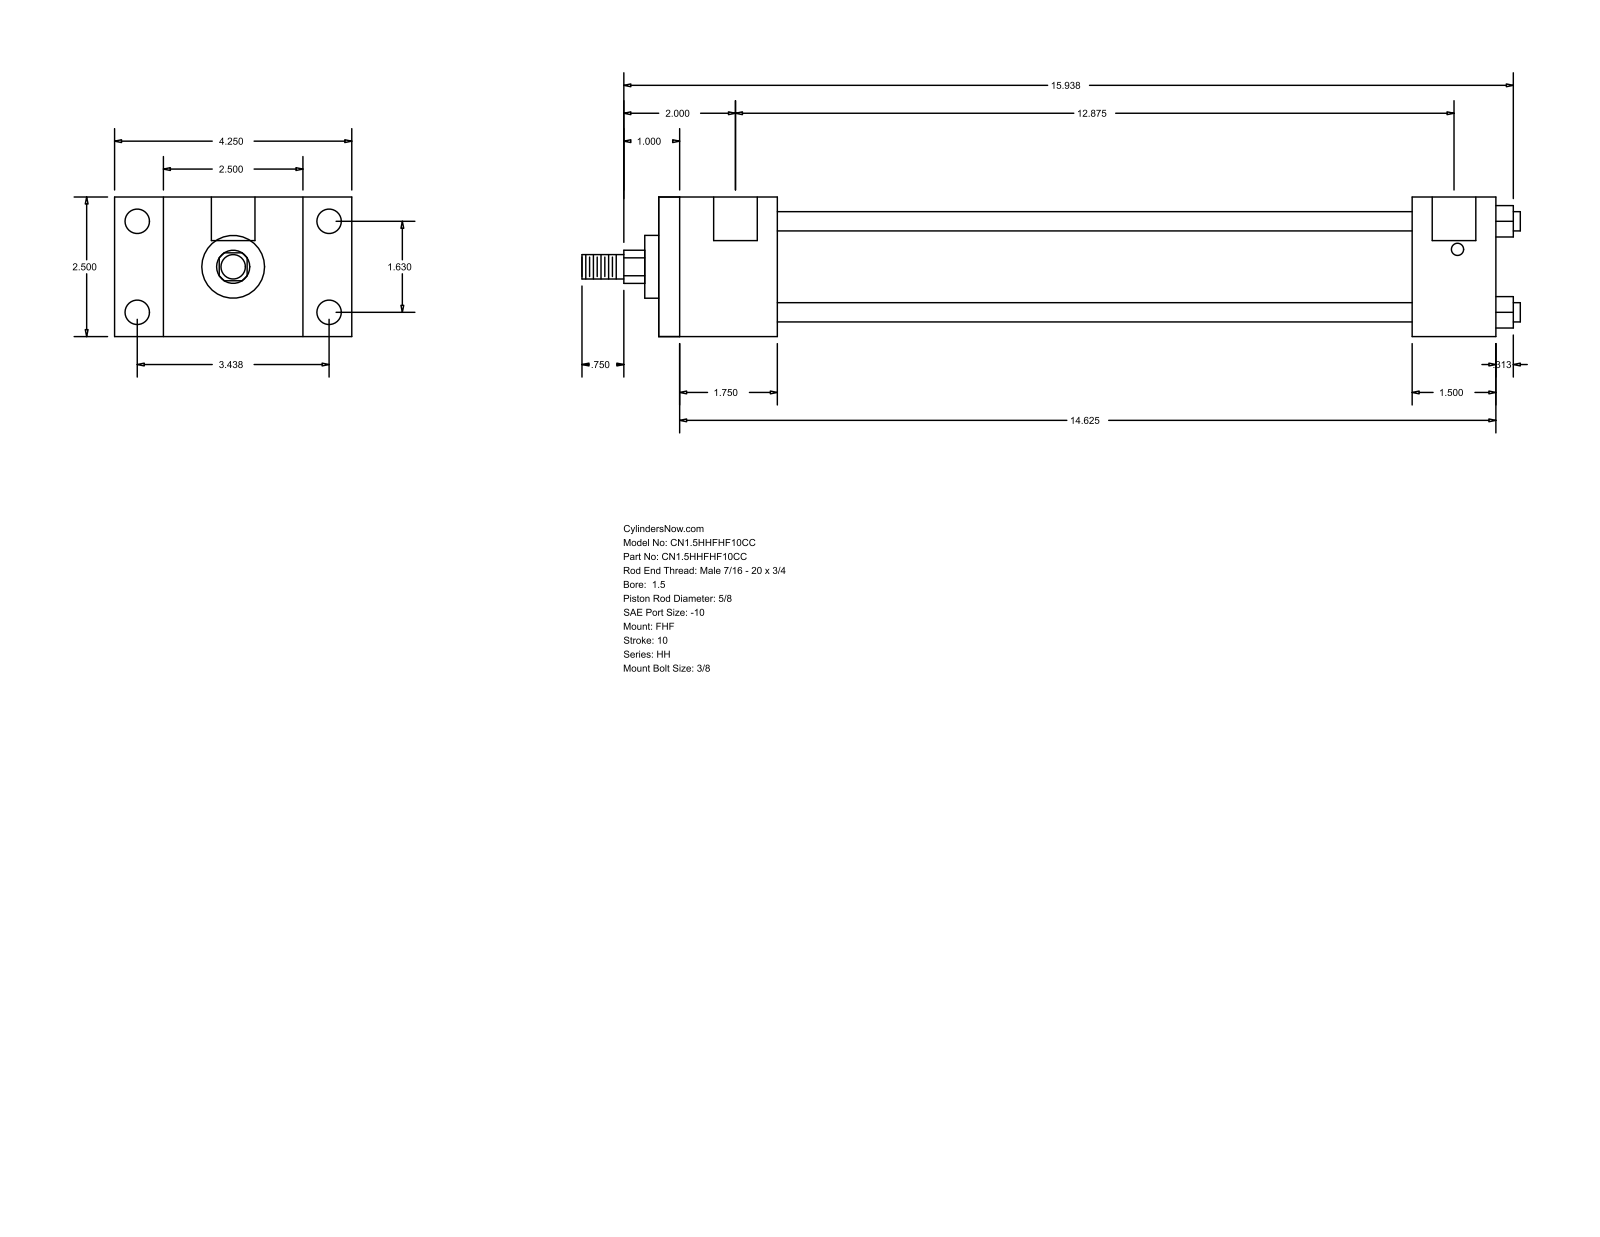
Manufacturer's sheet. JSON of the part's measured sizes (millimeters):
{"part_name": "HH_FHF__0150_0.625", "step_written_by": "GSSL Pune (CONFIG_CONTROL_DESIGN)", "units": "millimeters", "bodies": {"solids": 0, "faces": 88, "planar": 60, "cylindrical": 28, "other": 0}, "overall_size": [427.04, 107.95, 63.5], "round_holes": [[5.56, 4], [11.13, 4], [19.84, 2]], "round_bosses_or_shafts": [[8.76, 4], [44.45, 1], [28.57, 1], [15.88, 1], [11.11, 1]], "partial_cylinders_radius": [[7.54, 1]], "face_to_face_distances": [63.5, 22.23, 85.73, 53.97, 107.96, 381, 327.03, 342.89, 288.92, 38.11], "hole_center_spacings": [1.59, 41.4, 87.32, 96.64, 328.61, 330.2, 327.02]}
